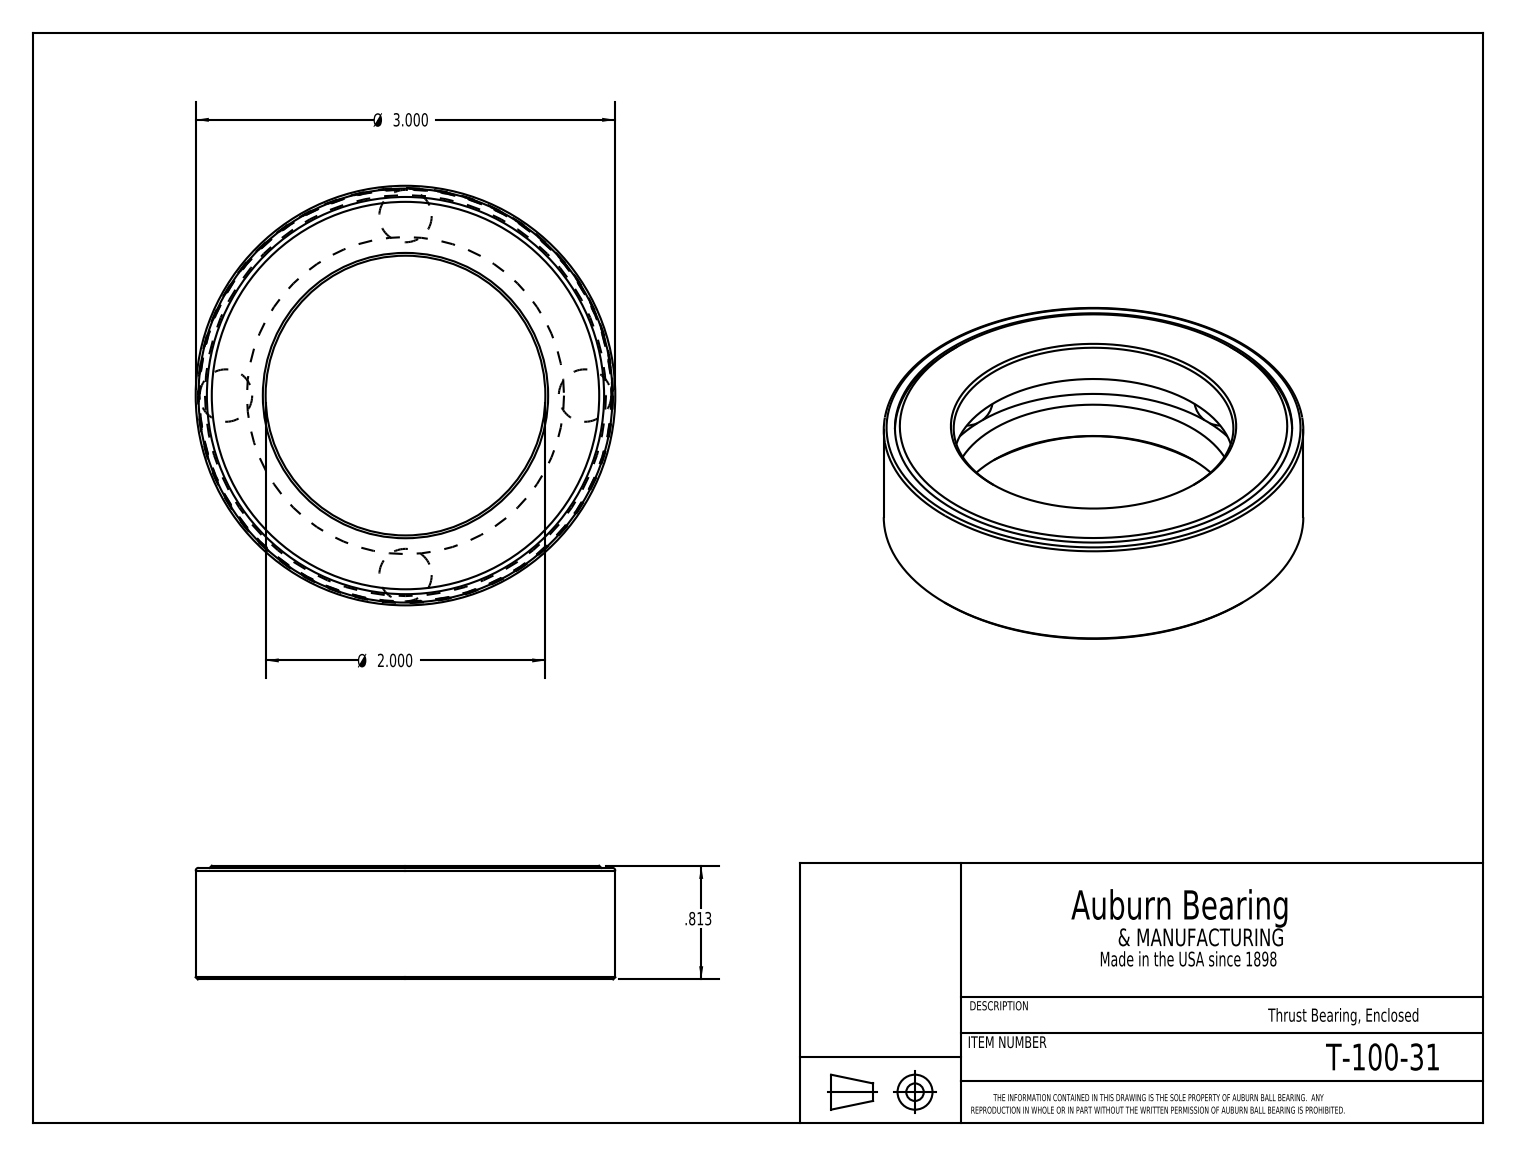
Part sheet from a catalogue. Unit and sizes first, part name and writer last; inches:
Units: inches
Overall size (bounding box): 3 × 3 × 0.813
Round holes (diameter × count): ⌀2 ×1, ⌀2.84 ×1, ⌀2.96 ×1
Round bosses / shafts (diameter × count): ⌀3 ×1, ⌀2.946 ×1
Main face-to-face distances: 0.813, 0.294, 0.519, 0.225, 0.798, 0.504, 0.279, 0.015, 0.778, 0.484
Volume: 2.155 in³ · Surface area: 36.71 in²
Bodies: 6 solids, 28 faces (9 planar, 7 cylindrical, 12 other)
Part name (STEP PRODUCT): T-100-31
STEP written by: SolidWorks 2016 (CONFIG_CONTROL_DESIGN)
